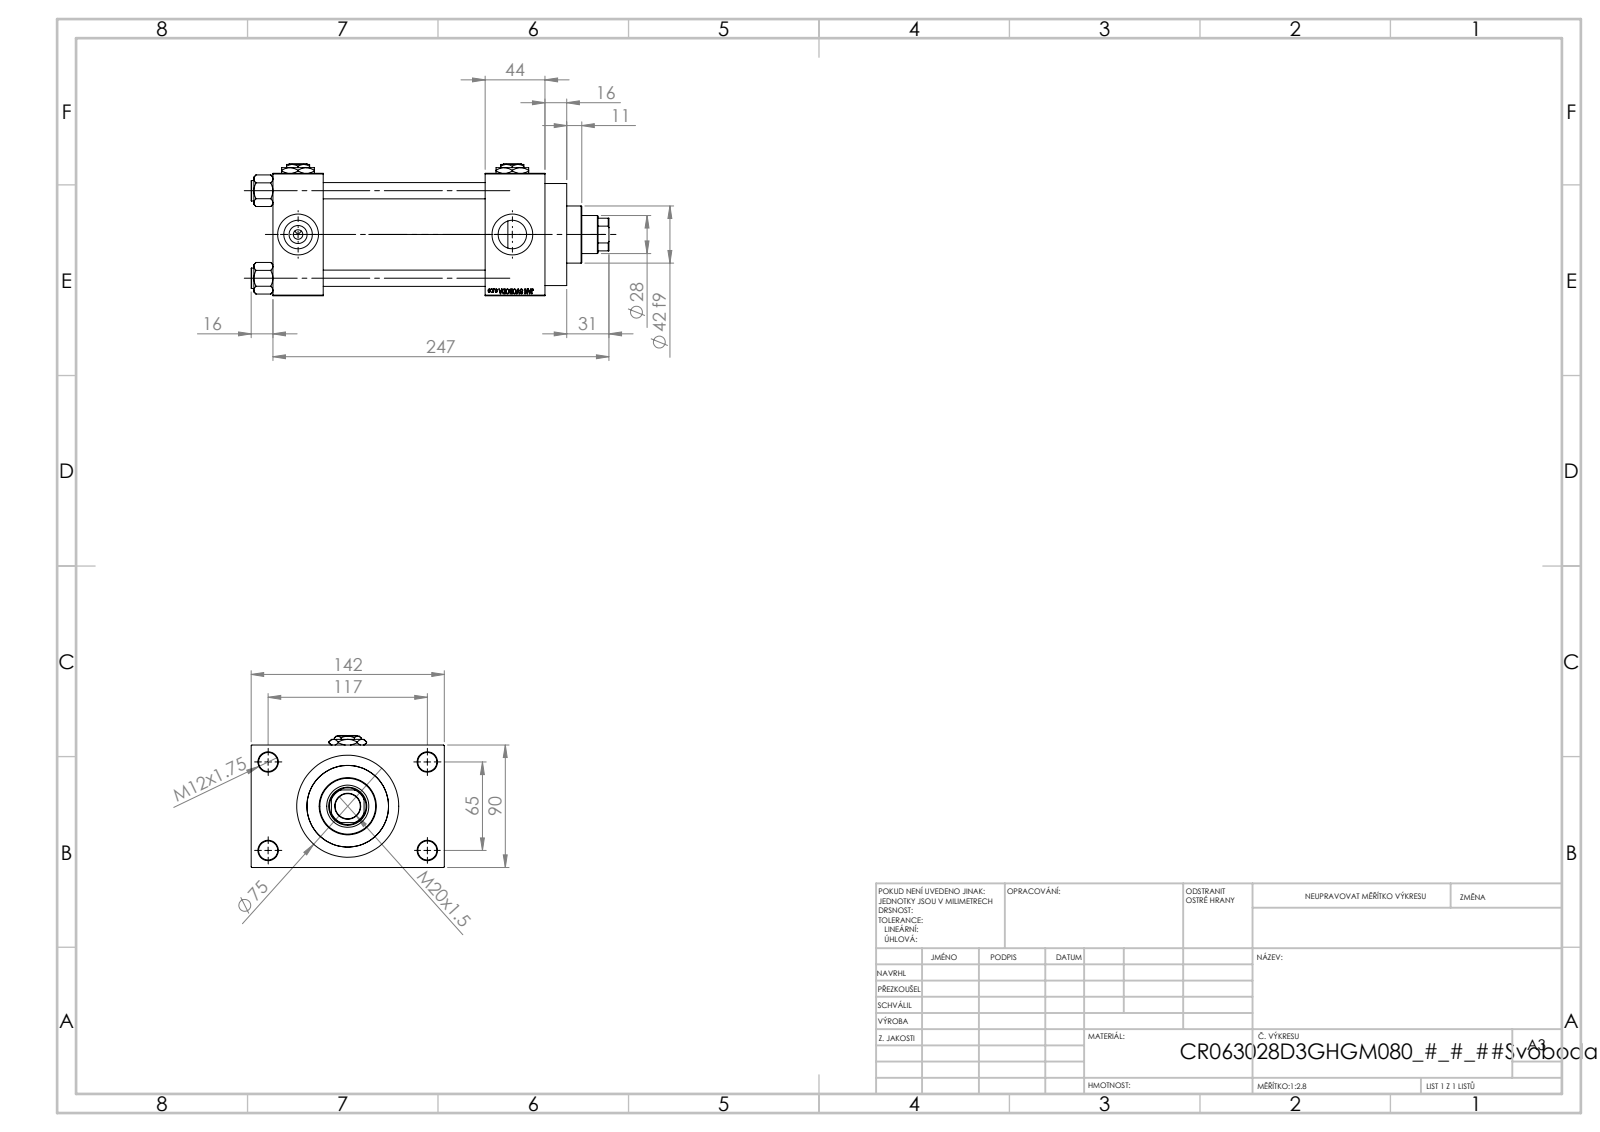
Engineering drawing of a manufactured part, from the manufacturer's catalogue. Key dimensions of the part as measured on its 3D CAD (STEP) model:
Part name (STEP PRODUCT): V215_VC_A; V215CR_D_Body; Zatka_pro_OIL_PORT; V215CR_VCP_D (+2 more)
STEP written by: SolidWorks 2019 (CONFIG_CONTROL_DESIGN)
Units: millimetres
Bodies: 13 solids, 1204 faces (545 planar, 99 cylindrical, 560 other)
Overall size (bounding box): 263 × 142 × 97
Volume: 1 192 000 mm³ · Surface area: 244 149 mm²
Round holes (diameter × count): ⌀12 ×4, ⌀14 ×4, ⌀20.96 ×4, ⌀30 ×4, ⌀7 ×3, ⌀18.5 ×1, ⌀28 ×1, ⌀31 ×1, ⌀50 ×1, ⌀60 ×1, ⌀63 ×1
Round bosses / shafts (diameter × count): ⌀15 ×4, ⌀75 ×1, ⌀69 ×1, ⌀42 ×1
Partial cylindrical surfaces — rounded edges, fillets, slot ends (radius × count): R13.5 ×1
Main face-to-face distances: 90, 119, 37, 156, 163, 200, 44, 26, 116, 16
Hole centre spacings: 26.35, 45.47, 64.3, 66.92, 69.81, 90.65, 111.34, 65
